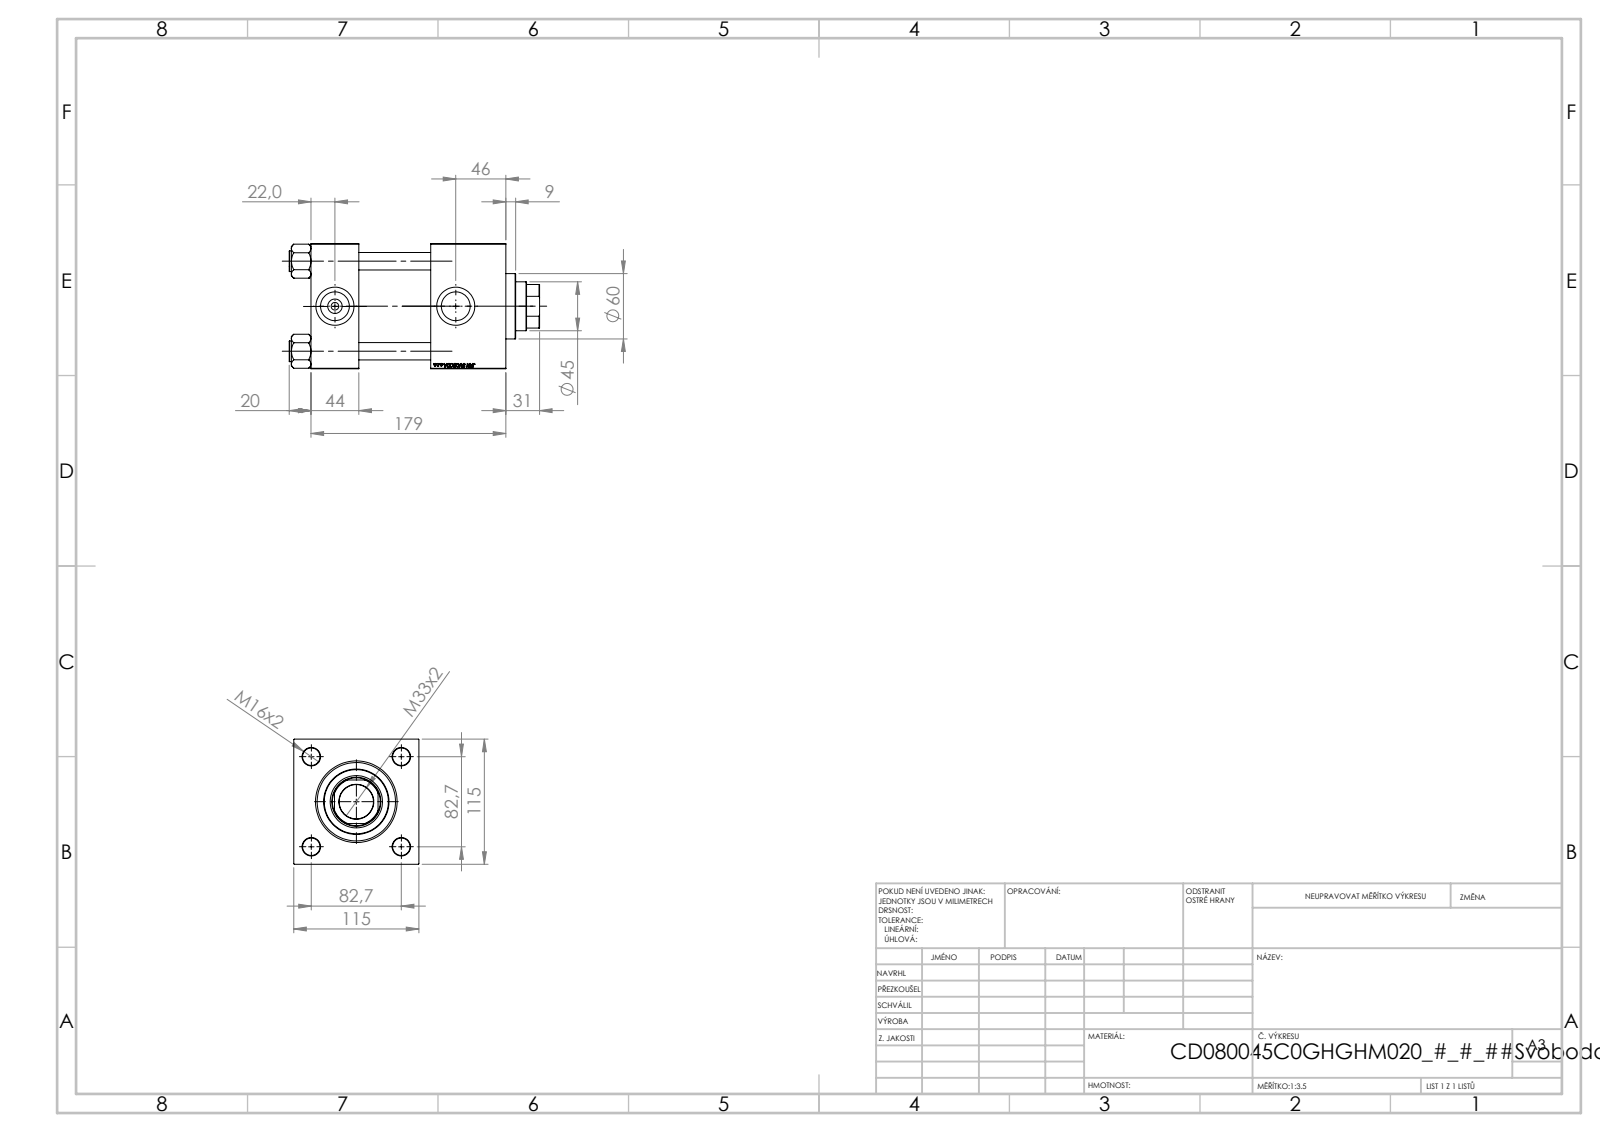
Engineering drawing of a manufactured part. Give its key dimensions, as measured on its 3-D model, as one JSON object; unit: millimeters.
{"part_name": "V215CD_VC_C; V215CD_C_TYCINKA; V215CD_VCP_C; V215CD_Body_C (+1 more)", "step_written_by": "SolidWorks 2019 (CONFIG_CONTROL_DESIGN)", "units": "millimeters", "bodies": {"solids": 11, "faces": 1196, "planar": 574, "cylindrical": 86, "other": 536}, "overall_size": [230, 115, 115], "volume_mm3": 1819000, "surface_area_mm2": 273876, "round_holes": [[16, 4], [7, 2], [26.44, 2], [35, 2], [31.5, 1], [45, 1], [48, 1], [61, 1], [72, 1], [80, 1]], "round_bosses_or_shafts": [[19, 4], [86, 1], [60, 1]], "partial_cylinders_radius": [[22, 1]], "face_to_face_distances": [115, 44, 110, 179, 135, 66, 69, 20, 150.3, 106.3], "hole_center_spacings": [58.48, 82.7, 116.96, 111]}
